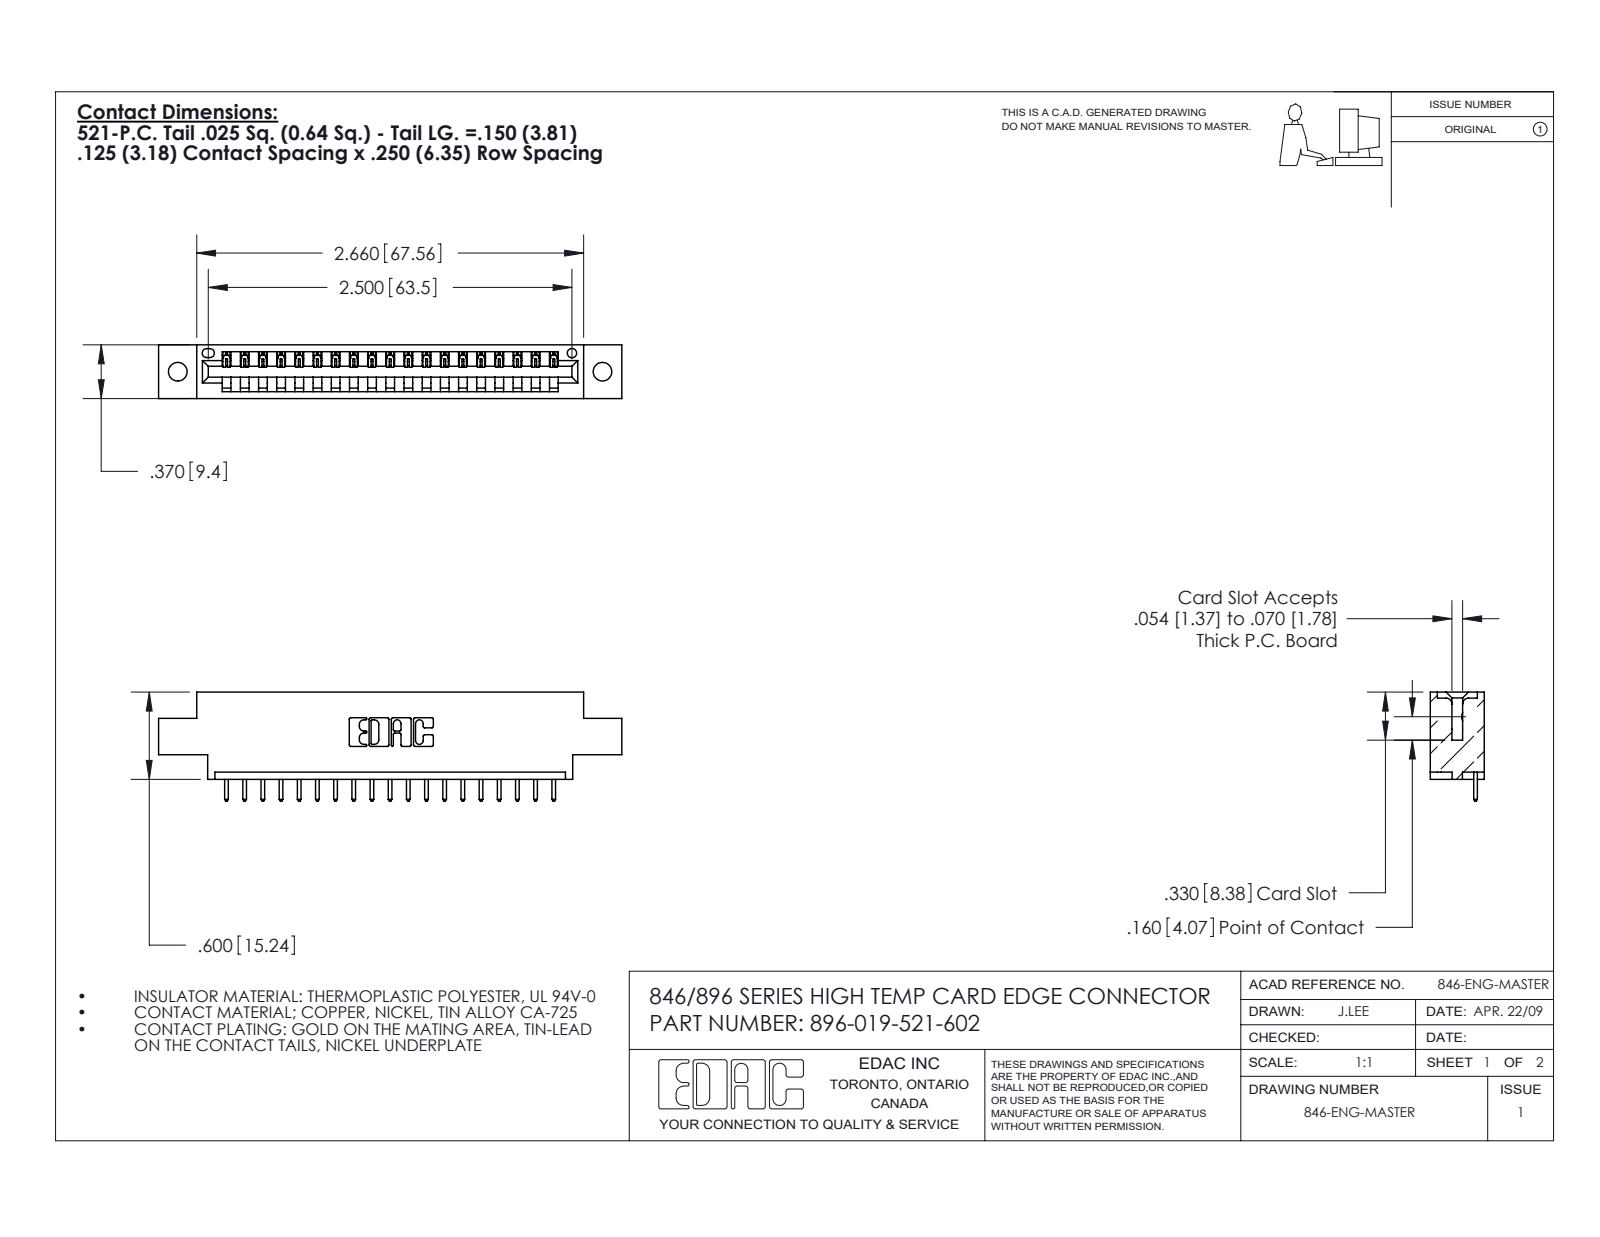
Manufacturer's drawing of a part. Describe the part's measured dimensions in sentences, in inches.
The part is named "346 Part_0.170 Offset - 0.128 Dia; 396-019-521-602; 345-292-001_345-293-121". Its 3-D file was written by "SolidWorks 2016 (CONFIG_CONTROL_DESIGN)". It is 20 solids with 1228 faces: 840 planar, 388 cylindrical and 0 other. Overall it measures 3.185 by 0.75 by 0.37 inches. Its volume is 0.448 cubic inches and its surface area 13.33 square inches. Round holes: 2 of diameter 0.128, 1 of diameter 0.064. Partial cylindrical surfaces (rounded edges, fillets, slot ends): 38 of radius 0.006, 38 of radius 0.01, 22 of radius 0.01, 6 of radius 0.007, 6 of radius 0.031, 3 of radius 0.026, 2 of radius 0.031, 2 of radius 0.04. The main face-to-face distances are 0.048, 0.322, 0.37, 0.25, 0.072, 0.298, 0.025, 0.148, 0.222, 0.1. The hole center spacings are 0.246, 2.713, 2.92.
